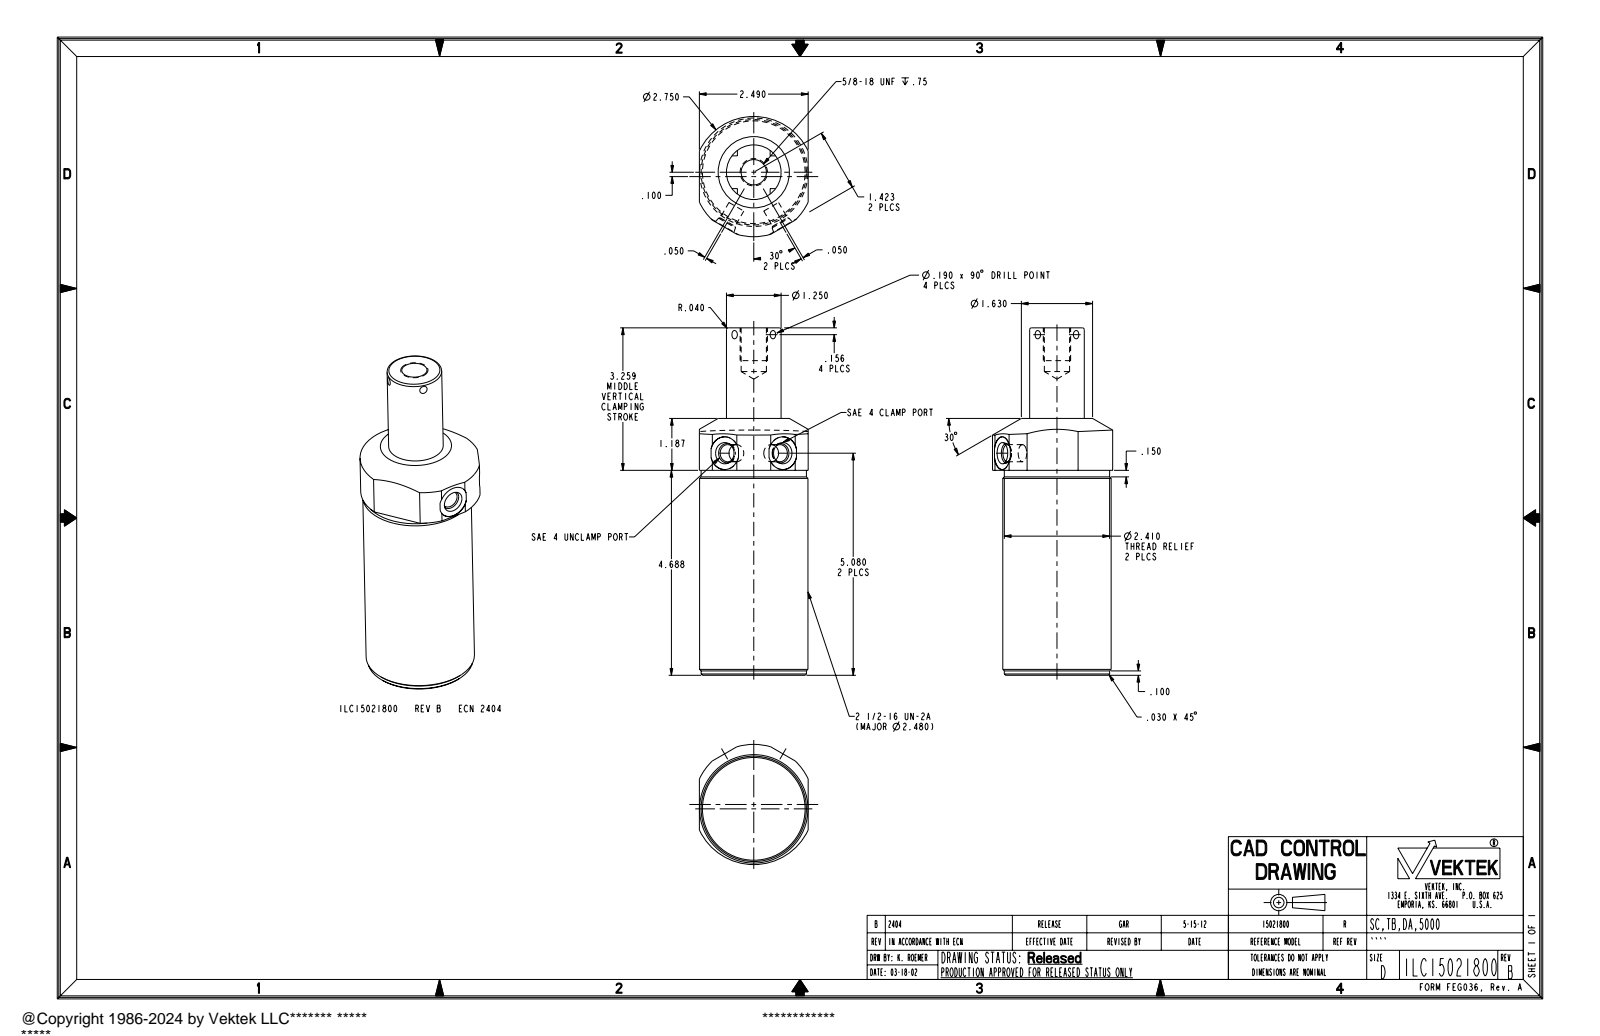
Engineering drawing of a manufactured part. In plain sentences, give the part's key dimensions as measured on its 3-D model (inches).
The part is named "ILC15021800". Its 3-D file was written by "PRO/ENGINEER BY PARAMETRIC TECHNOLOGY CORPORATION, 2007460 (AUTOMOTIVE_DESIGN_CC2)". It is 1 solid with 67 faces: 15 planar, 24 cylindrical and 28 other. Overall it measures 7.947 by 2.75 by 2.49 inches. Its volume is 30.83 cubic inches and its surface area 68.81 square inches. Round holes: 2 of diameter 0.392, 2 of diameter 0.75, 1 of diameter 0.578. Round bosses or shafts: 1 of diameter 2.48, 1 of diameter 2.41, 1 of diameter 1.25, 1 of diameter 0.625. Partial cylindrical surfaces (rounded edges, fillets, slot ends): 1 of radius 1.375. The main face-to-face distances are 4.688, 2.49, 5.875, 1.187, 7.947, 3.259, 2.072, 0.53, 0.54, 7.197.
